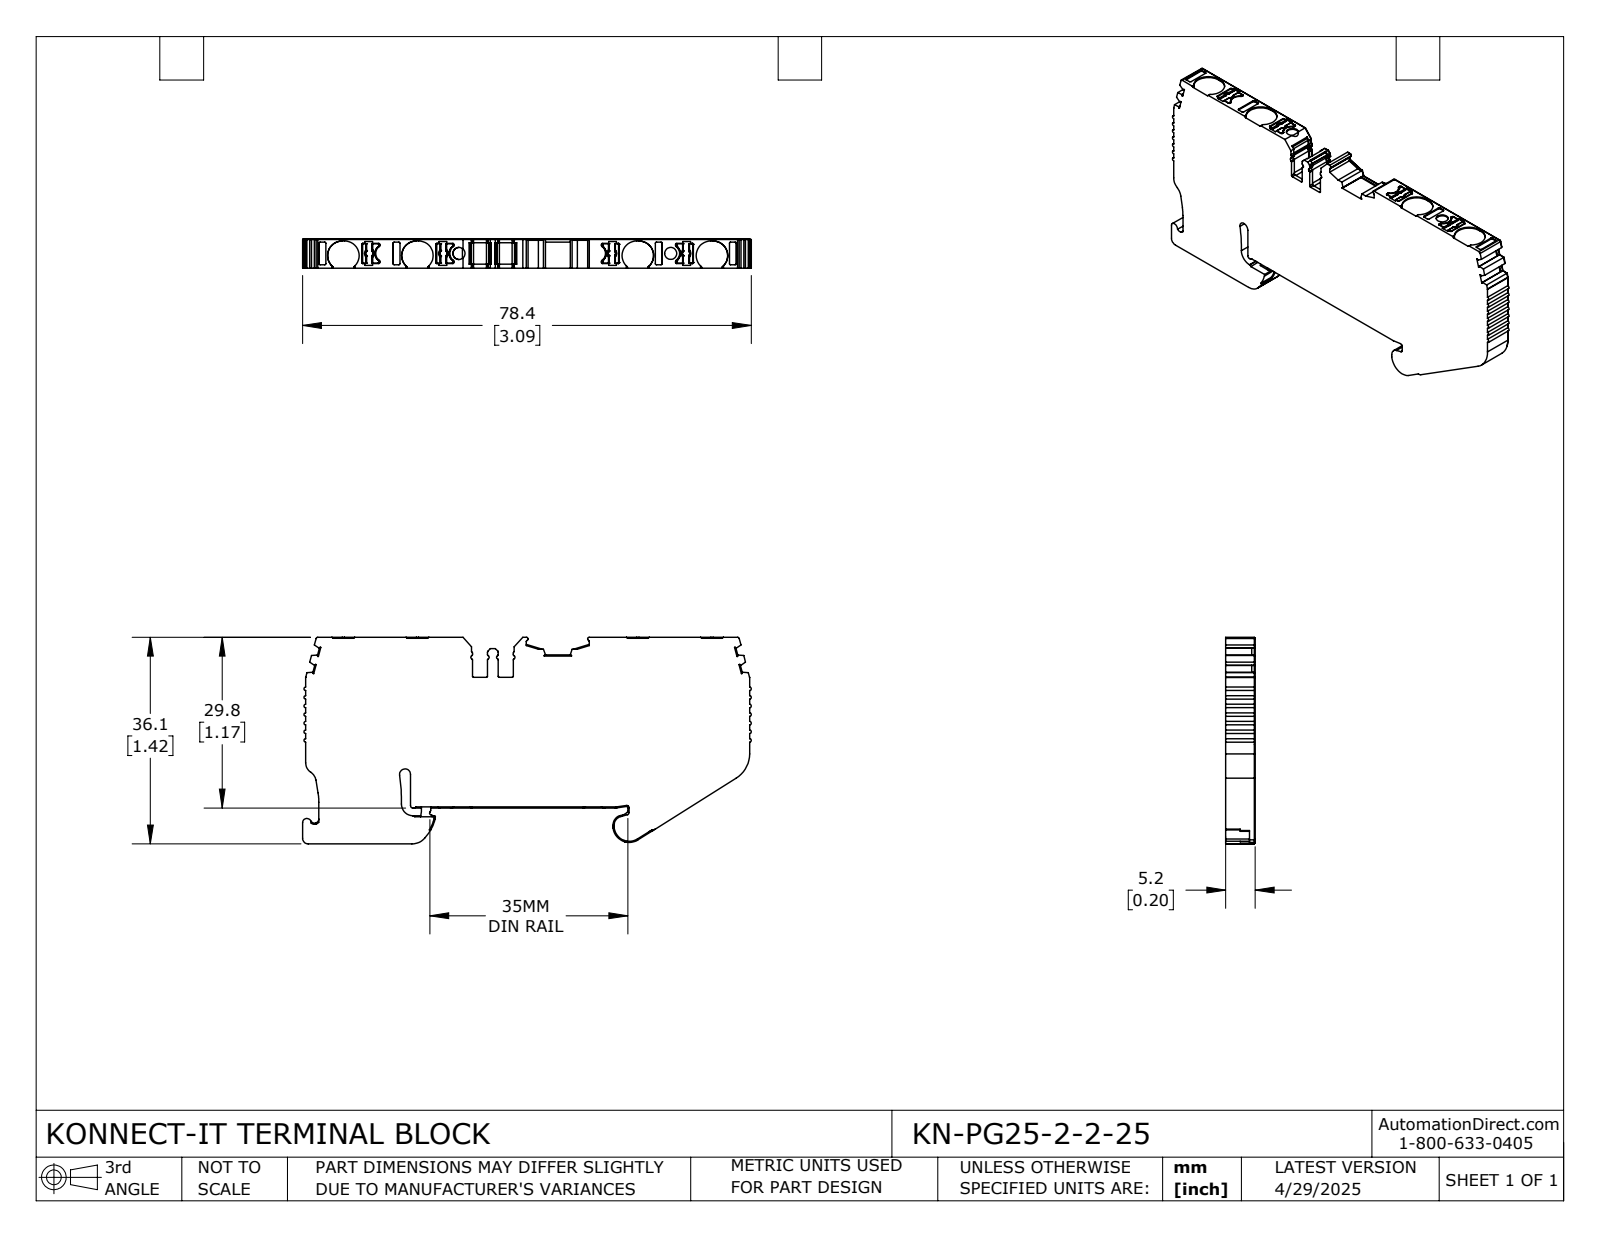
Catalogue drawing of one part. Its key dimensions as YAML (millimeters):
part_name: "KN-PG25-2-2-25"
step_written_by: "SolidWorks 2024 (CONFIG_CONTROL_DESIGN)"
units: millimeters
bodies: {solids: 1, faces: 791, planar: 409, cylindrical: 313, other: 69}
overall_size: [78.36, 36.07, 5.15]
volume: 11929
surface_area: 6263
round_holes:
  - {diameter: 2.1, count: 2}
partial_cylinders:
  - {radius: 0.2, count: 77}
  - {radius: 0.3, count: 42}
  - {radius: 0.1, count: 21}
  - {radius: 0.4, count: 17}
  - {radius: 0.15, count: 16}
  - {radius: 0.5, count: 16}
  - {radius: 1, count: 8}
  - {radius: 2.55, count: 8}
face_to_face_distances: [5.15, 29.61, 29.81, 6.26, 35.87, 36.07, 6.46, 29.41, 77.52, 1.2]
hole_center_spacings: [36.98]
